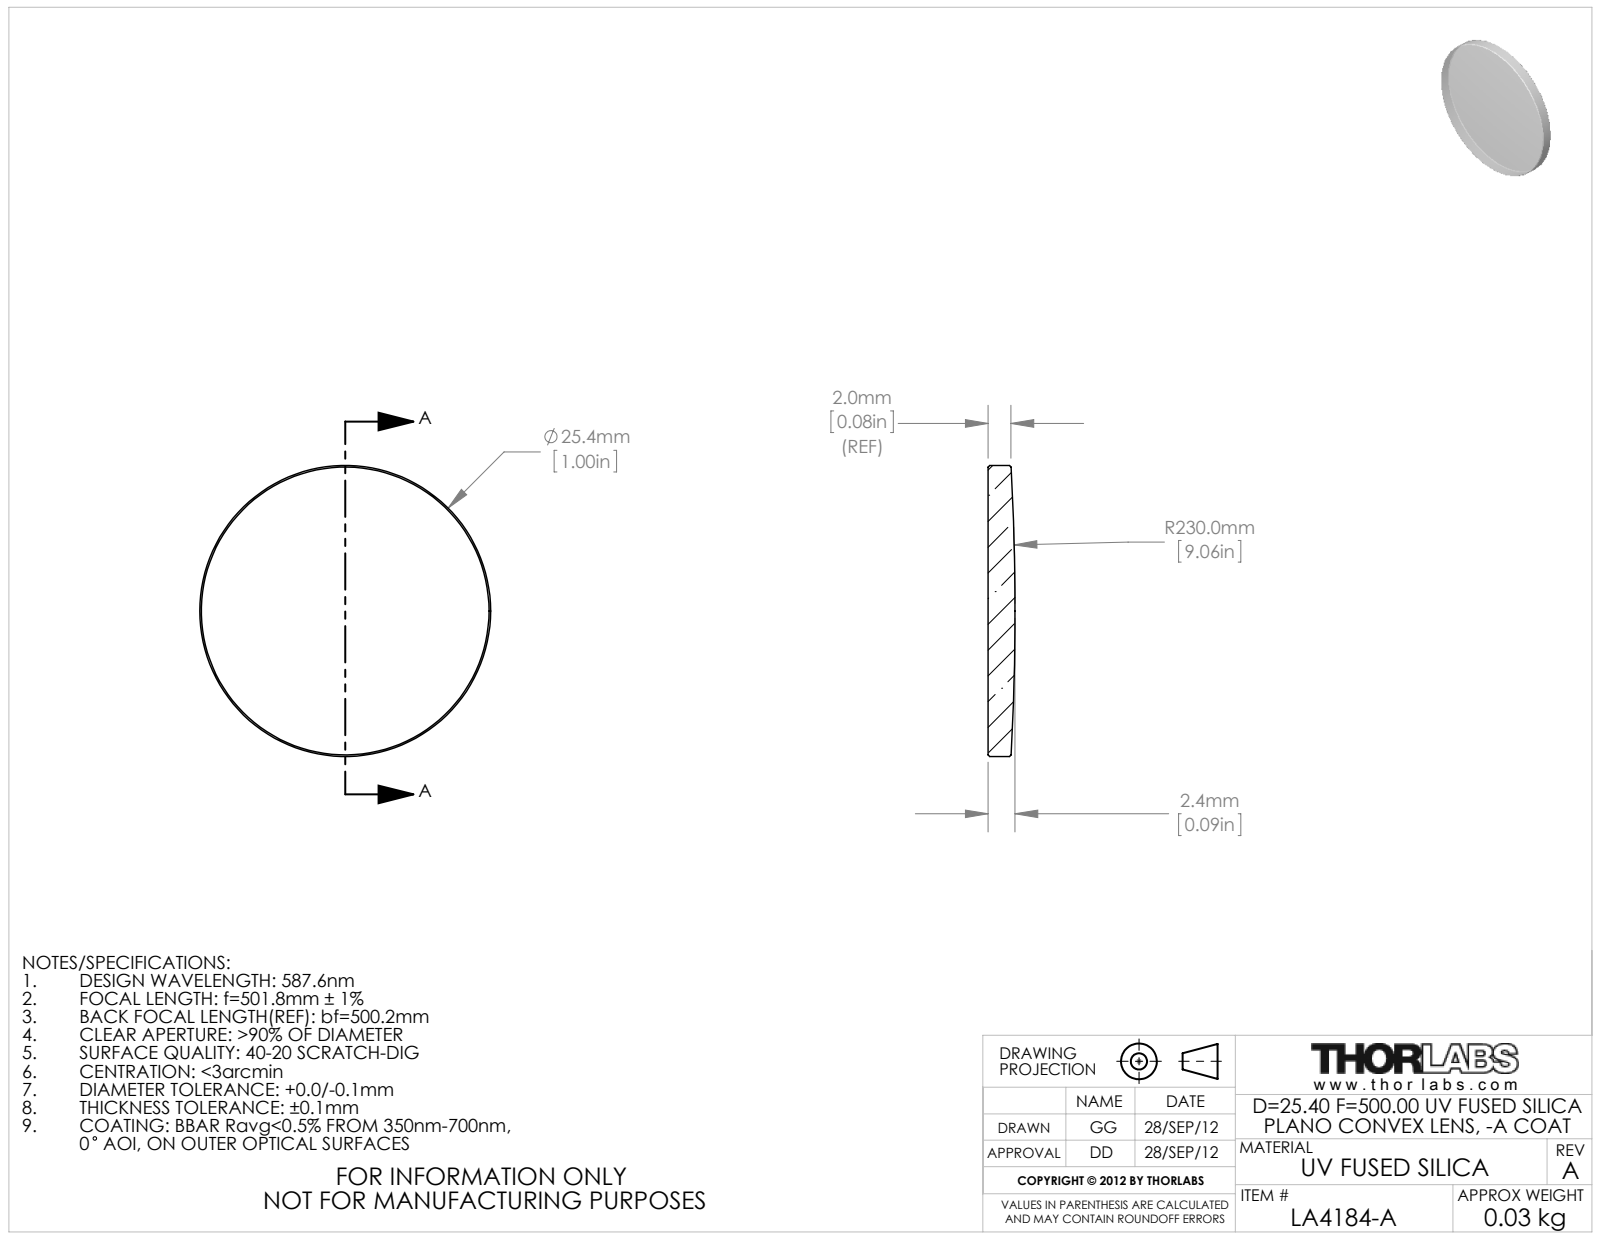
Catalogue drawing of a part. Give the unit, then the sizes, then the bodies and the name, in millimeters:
Units: millimetres
Overall size (bounding box): 25.4 × 25.4 × 2.35
Round bosses / shafts (diameter × count): ⌀25.4 ×1
Volume: 1 101 mm³ · Surface area: 1 161 mm²
Bodies: 1 solid, 9 faces (1 planar, 2 cylindrical, 6 other)
Part name (STEP PRODUCT): 25002-E0W
STEP written by: SolidWorks 2011 (CONFIG_CONTROL_DESIGN)
